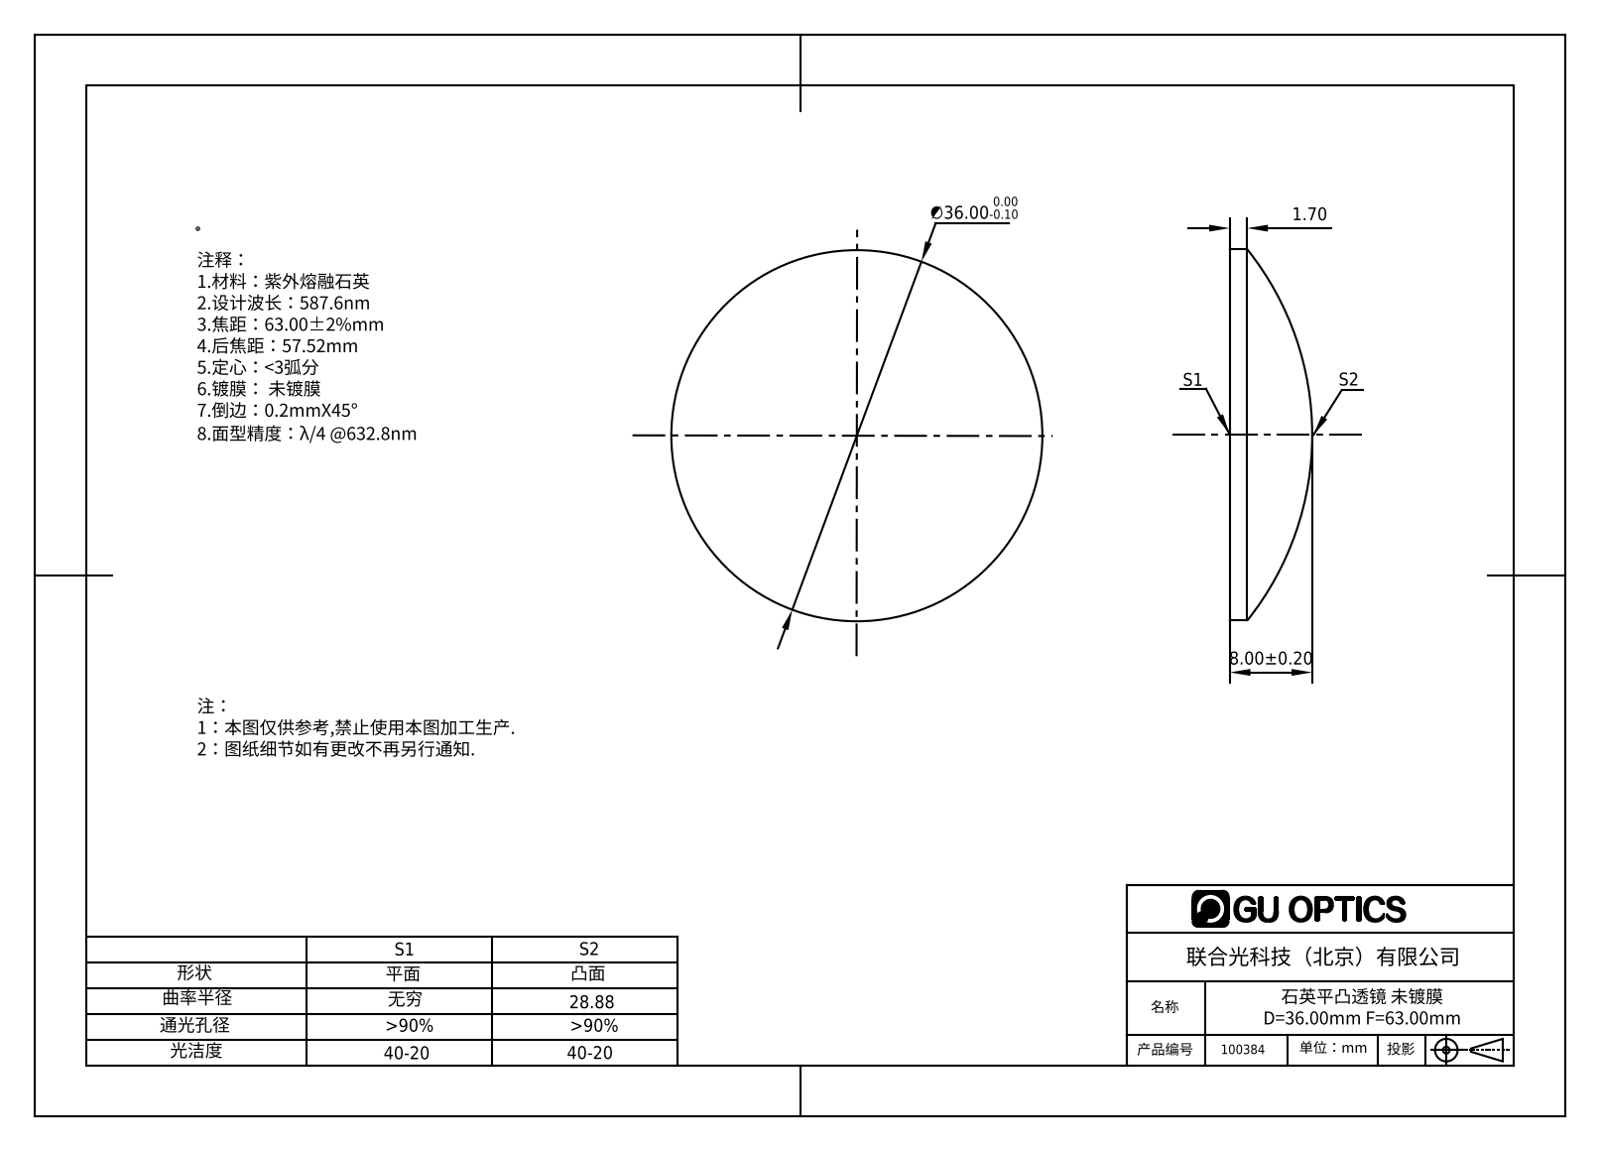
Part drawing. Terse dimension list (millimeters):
name: 100384
written by: SolidWorks 2016 (AUTOMOTIVE_DESIGN)
unit: mm
bodies: 1 solid, 5 faces (1 planar, 2 cylindrical, 2 other)
size: 36 × 36 × 8
volume: 5 068 mm³; area: 2 353 mm²
bosses: 1× ⌀36
